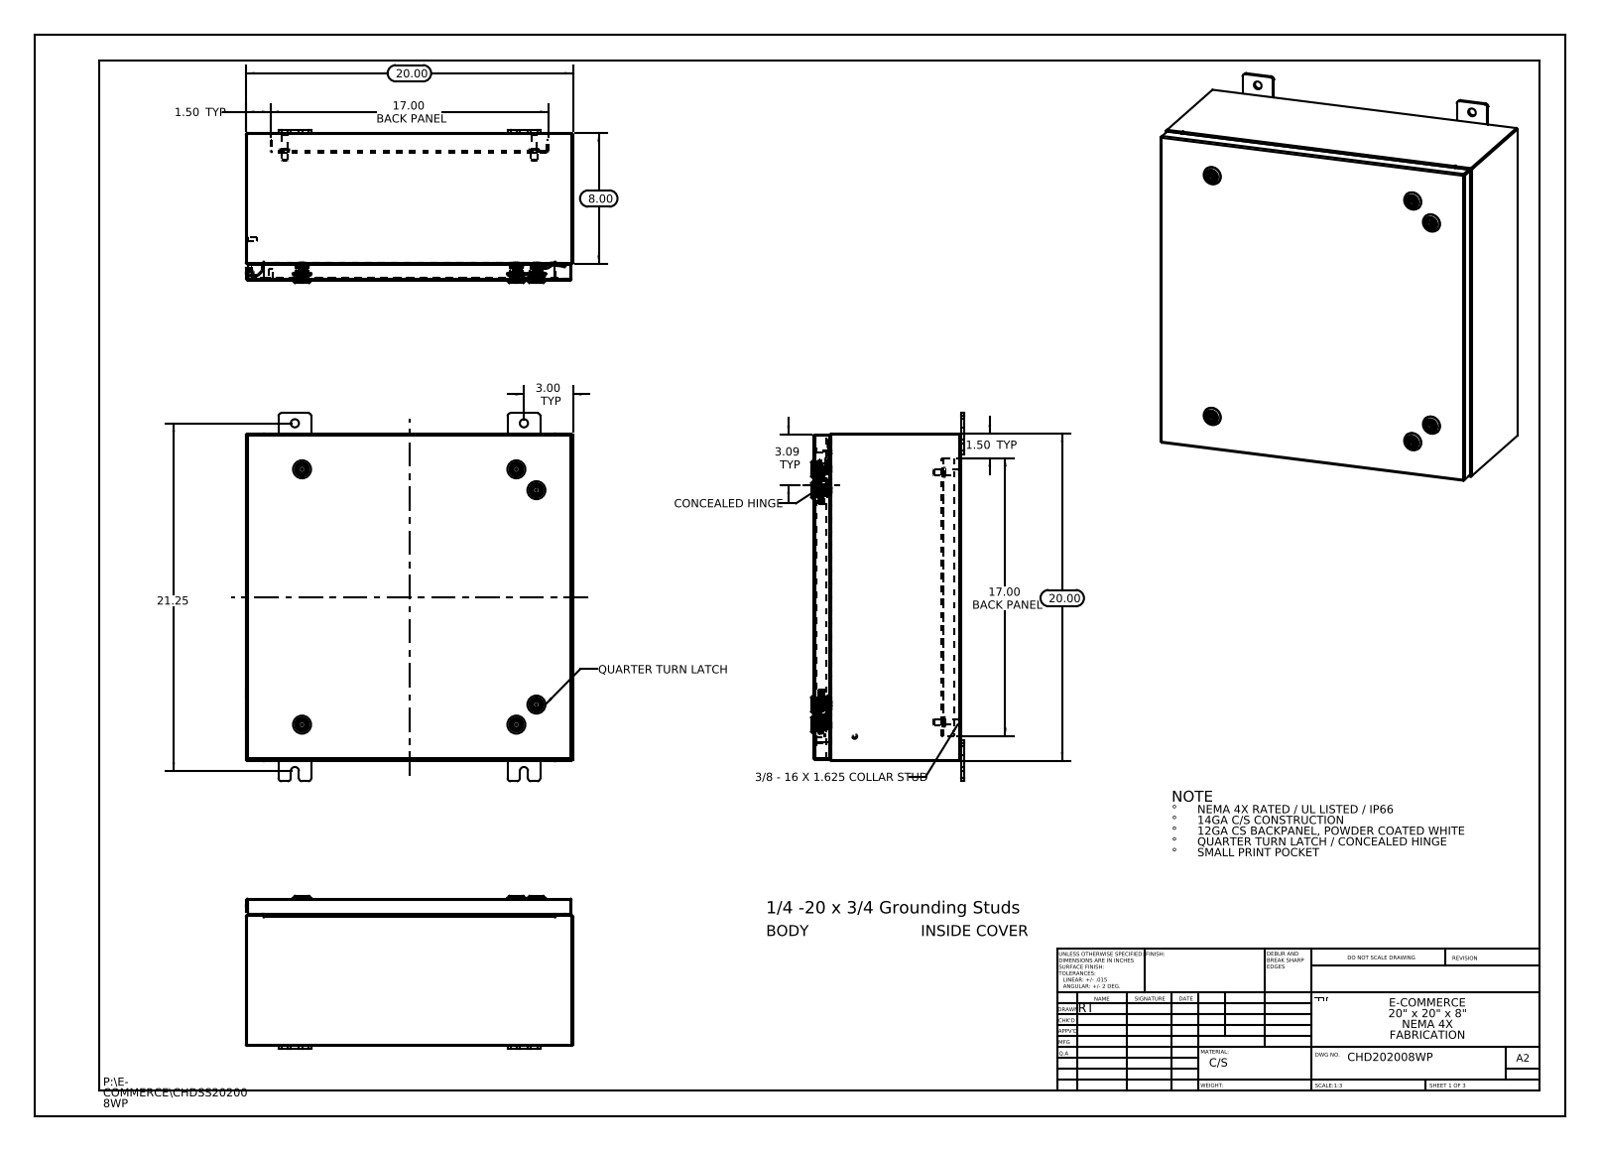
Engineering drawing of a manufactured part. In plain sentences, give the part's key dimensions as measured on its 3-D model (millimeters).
The part is named "Quarter-20 CD Stud; CHDSS202008WP Mounting Feet; CHDSS202008WP Top; CHDSS202008WP Bottom (+8 more)". Its 3-D file was written by "SolidWorks 2013 (CONFIG_CONTROL_DESIGN)". It is 55 solids with 5420 faces: 1592 planar, 1692 cylindrical and 2136 other. Overall it measures 571.5 by 508 by 237.6 millimeters. Its volume is 2 674 000 cubic millimeters and its surface area 2 637 000 square millimeters. Round holes: 8 of diameter 12.7, 6 of diameter 5, 6 of diameter 10, 6 of diameter 10.2, 6 of diameter 16, 6 of diameter 20, 4 of diameter 3.5, 2 of diameter 5.4. Round bosses or shafts: 8 of diameter 6, 6 of diameter 28, 6 of diameter 19.8, 6 of diameter 15.9, 6 of diameter 15.5, 6 of diameter 13.5, 6 of diameter 10, 6 of diameter 2.9. Partial cylindrical surfaces (rounded edges, fillets, slot ends): 198 of radius 0.2, 198 of radius 3, 72 of radius 0.7, 24 of radius 0.5, 24 of radius 4.8, 24 of radius 5, 20 of radius 0.3, 18 of radius 2.2. The main face-to-face distances are 1.9, 506.1, 1.9, 228.9, 226.9, 227, 225.1, 504.2, 508, 2.6. The hole center spacings are 332.7, 47.2, 77.9, 355.6, 365.2, 387.4, 387.4, 396.2.
